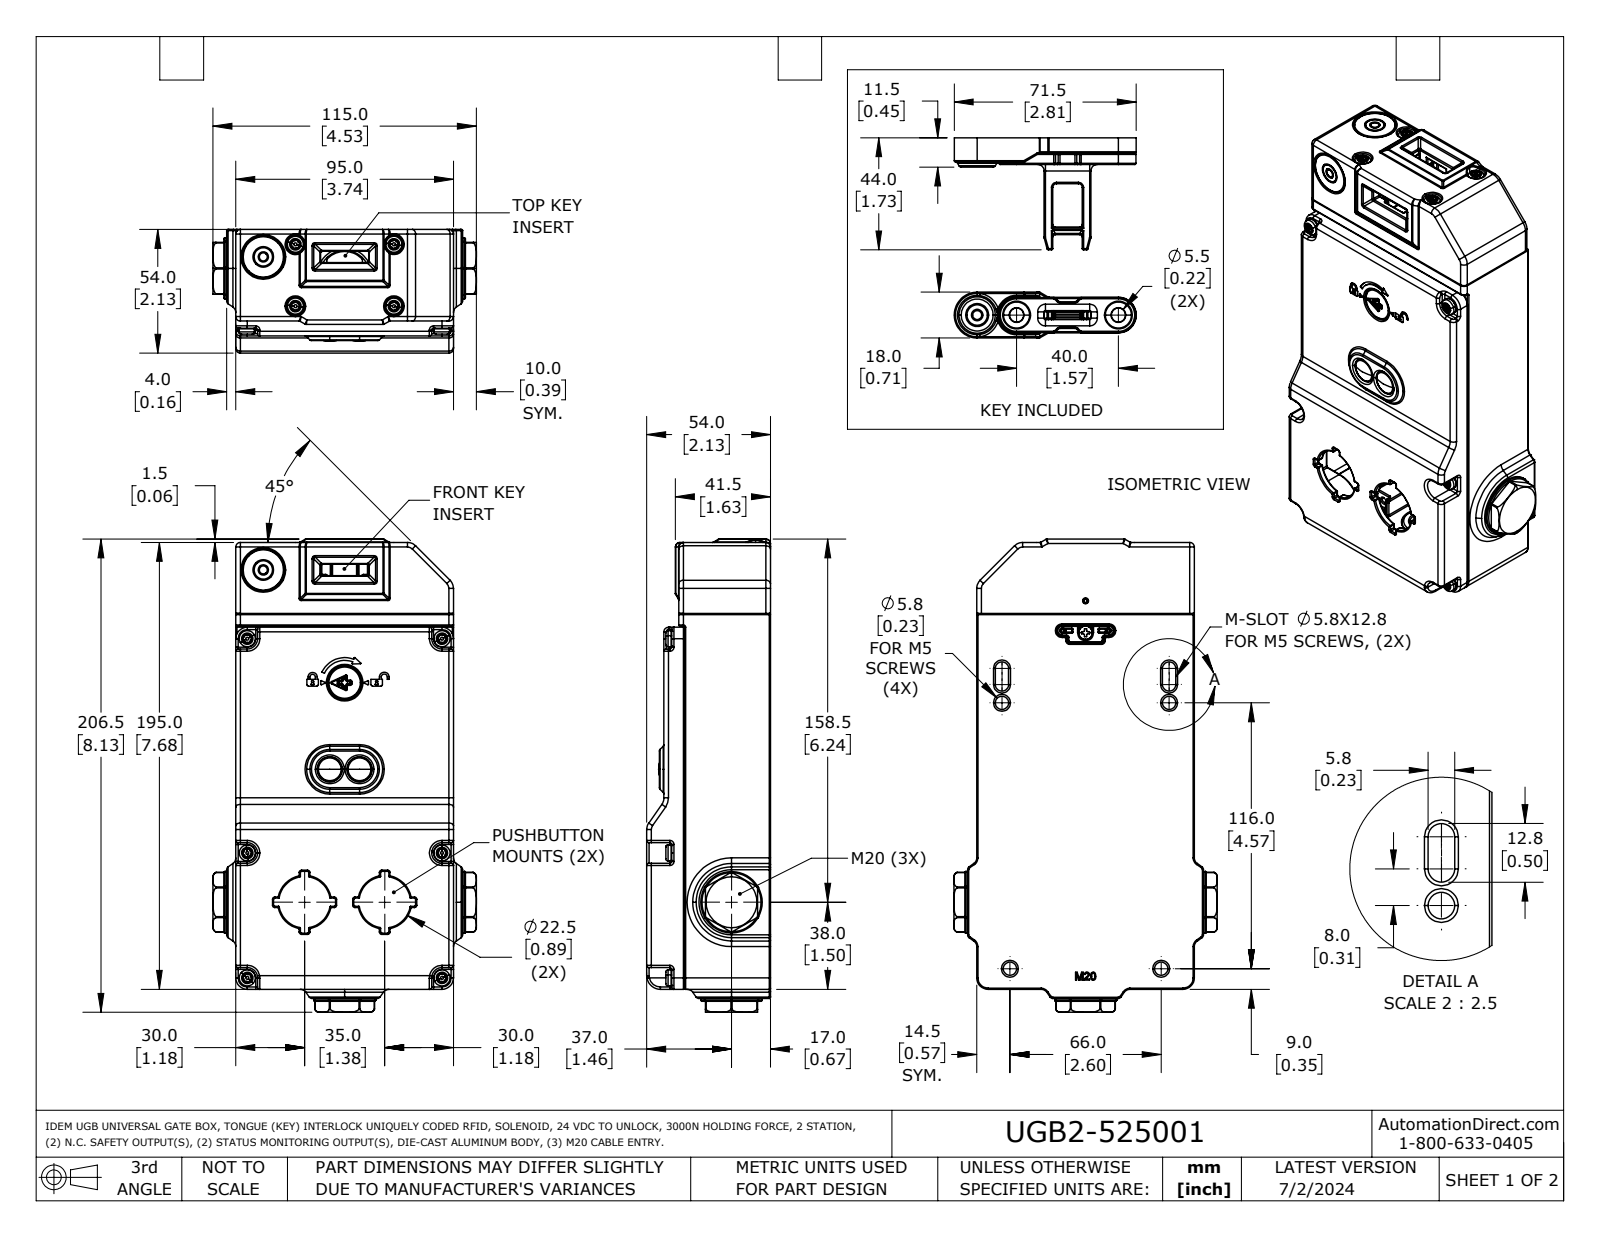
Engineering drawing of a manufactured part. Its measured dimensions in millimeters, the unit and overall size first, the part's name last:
Units: millimetres
Overall size (bounding box): 219 × 115 × 54
Round holes (diameter × count): ⌀3.3 ×10, ⌀4 ×10, ⌀2.5 ×8, ⌀4.5 ×8, ⌀8 ×8, ⌀4.2 ×4, ⌀5 ×4, ⌀5.5 ×4, ⌀5.8 ×4, ⌀12 ×4, ⌀9 ×3, ⌀2.2 ×2
Round bosses / shafts (diameter × count): ⌀3.5 ×12, ⌀7 ×10, ⌀1.3 ×10, ⌀6.2 ×6, ⌀6 ×5, ⌀18 ×3, ⌀26.8 ×2, ⌀19.4 ×2
Partial cylindrical surfaces — rounded edges, fillets, slot ends (radius × count): R0.5 ×626, R1 ×205, R0.2 ×127, R0.3 ×106, R2 ×36, R0.4 ×22, R0.7 ×20, R0.8 ×16
Main face-to-face distances: 3, 2.2, 92, 7.5, 95, 46.5, 44.3, 43.5, 51, 4.5
Hole centre spacings: 25.39, 41.86, 75.61, 15.5, 36.39, 58.01, 85, 2.83
Volume: 286 998 mm³ · Surface area: 179 895 mm²
Bodies: 26 solids, 5077 faces (1147 planar, 2081 cylindrical, 1849 other)
Part name (STEP PRODUCT): 525001 UGB2-KLTM-RFID with Manual Override
STEP written by: SolidWorks 2021 (CONFIG_CONTROL_DESIGN)
